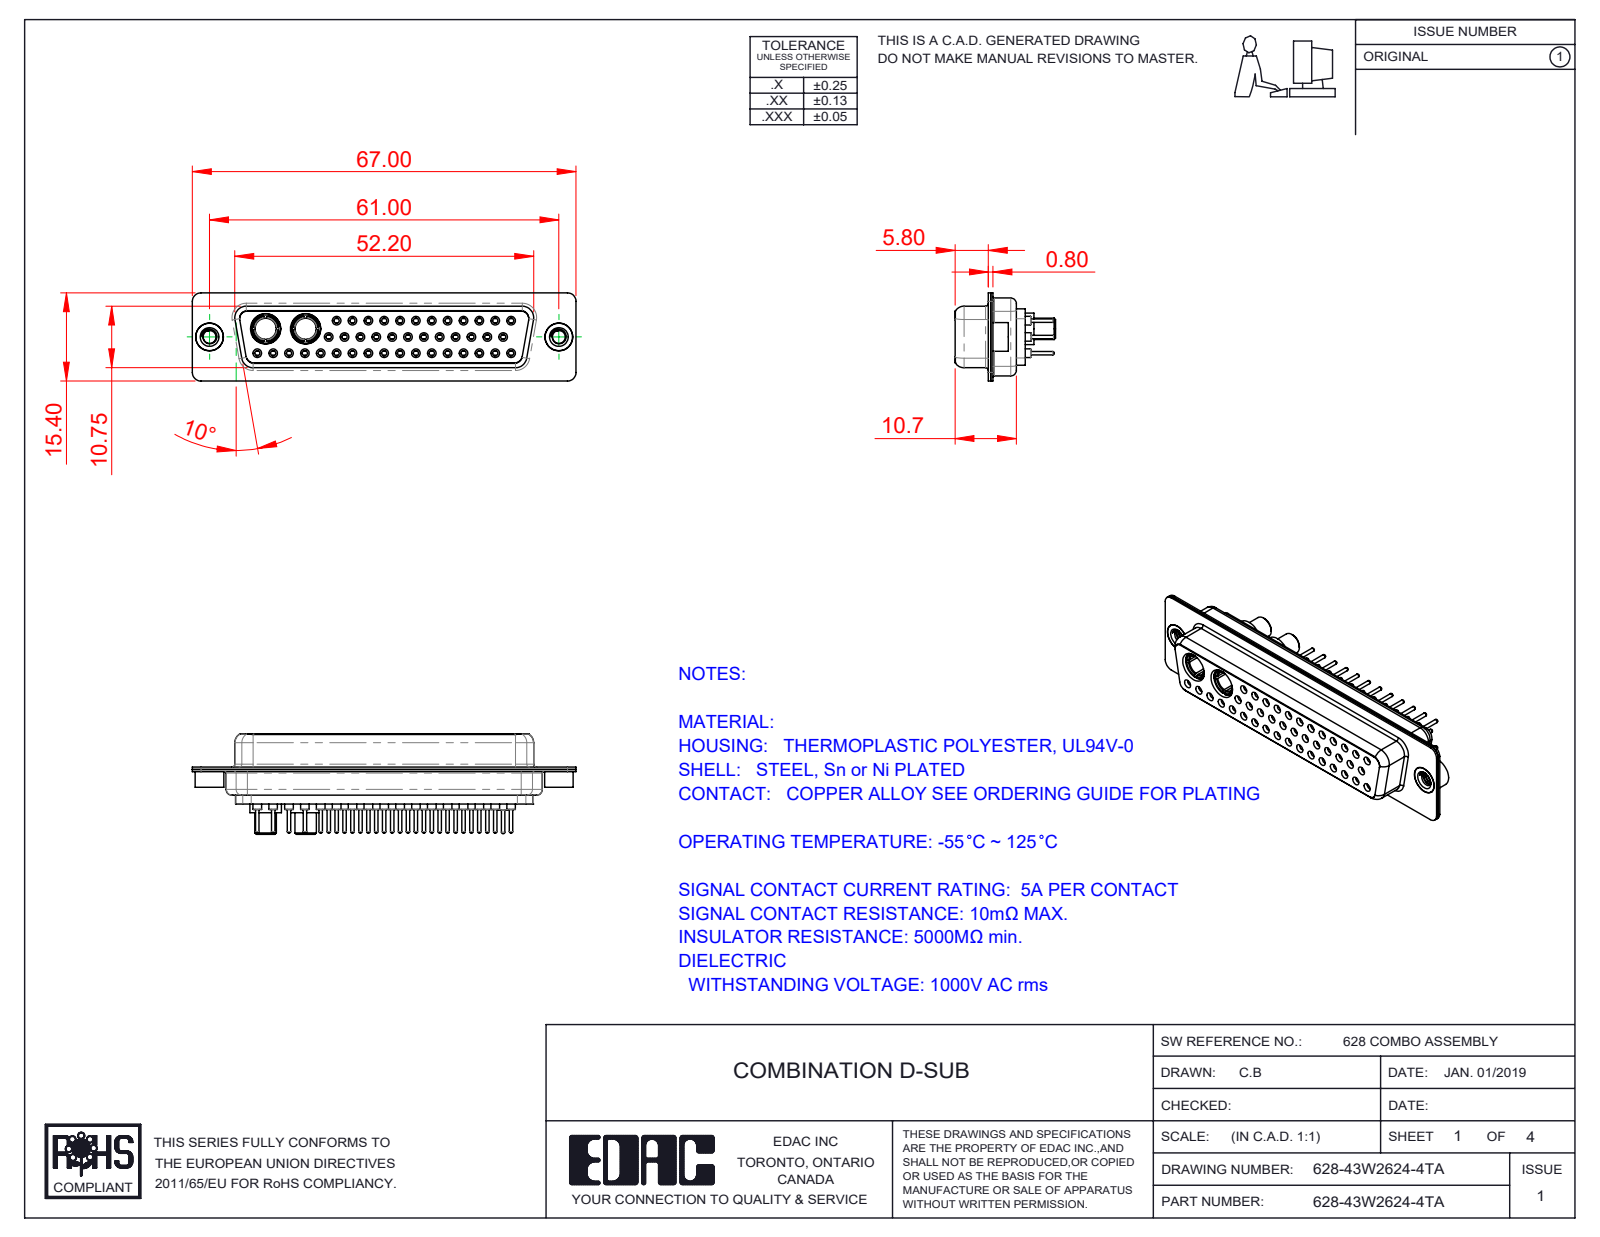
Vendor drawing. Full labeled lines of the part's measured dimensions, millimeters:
Part name (STEP PRODUCT): 628Combo Shell Front_50 Contacts; 628Combo Threaded Rivet_A; 628Combo Contact Row 1_24; 628-43W2624-4TA (+5 more)
STEP written by: SolidWorks 2016 (CONFIG_CONTROL_DESIGN)
Units: millimetres
Bodies: 50 solids, 2682 faces (740 planar, 964 cylindrical, 978 other)
Overall size (bounding box): 67 × 17.55 × 15.4
Volume: 7 051 mm³ · Surface area: 14 622 mm²
Round holes (diameter × count): ⌀0.9 ×41, ⌀1.1 ×41, ⌀1.5 ×41, ⌀2 ×41, ⌀1.6 ×29, ⌀1.7 ×12, ⌀4.85 ×4, ⌀2.26 ×2, ⌀3.7 ×2, ⌀4 ×2, ⌀4.05 ×2, ⌀5.3 ×2
Round bosses / shafts (diameter × count): ⌀2.2 ×41, ⌀0.6 ×41, ⌀1.6 ×12, ⌀5.5 ×2, ⌀5.2 ×2, ⌀5 ×2, ⌀4.96 ×2, ⌀4.95 ×2
Partial cylindrical surfaces — rounded edges, fillets, slot ends (radius × count): R1.5 ×16, R1.35 ×12, R2 ×12, R1.6 ×8, R0.25 ×4, R0.5 ×4, R0.6 ×4, R0.65 ×4
Main face-to-face distances: 0.4, 6.45, 11.33, 6.05, 1.87, 10.35, 10.93, 12.25, 6.2, 5.8
Hole centre spacings: 2.77, 3.16, 5.54, 8.31, 11.08, 13.85, 16.62, 19.39
